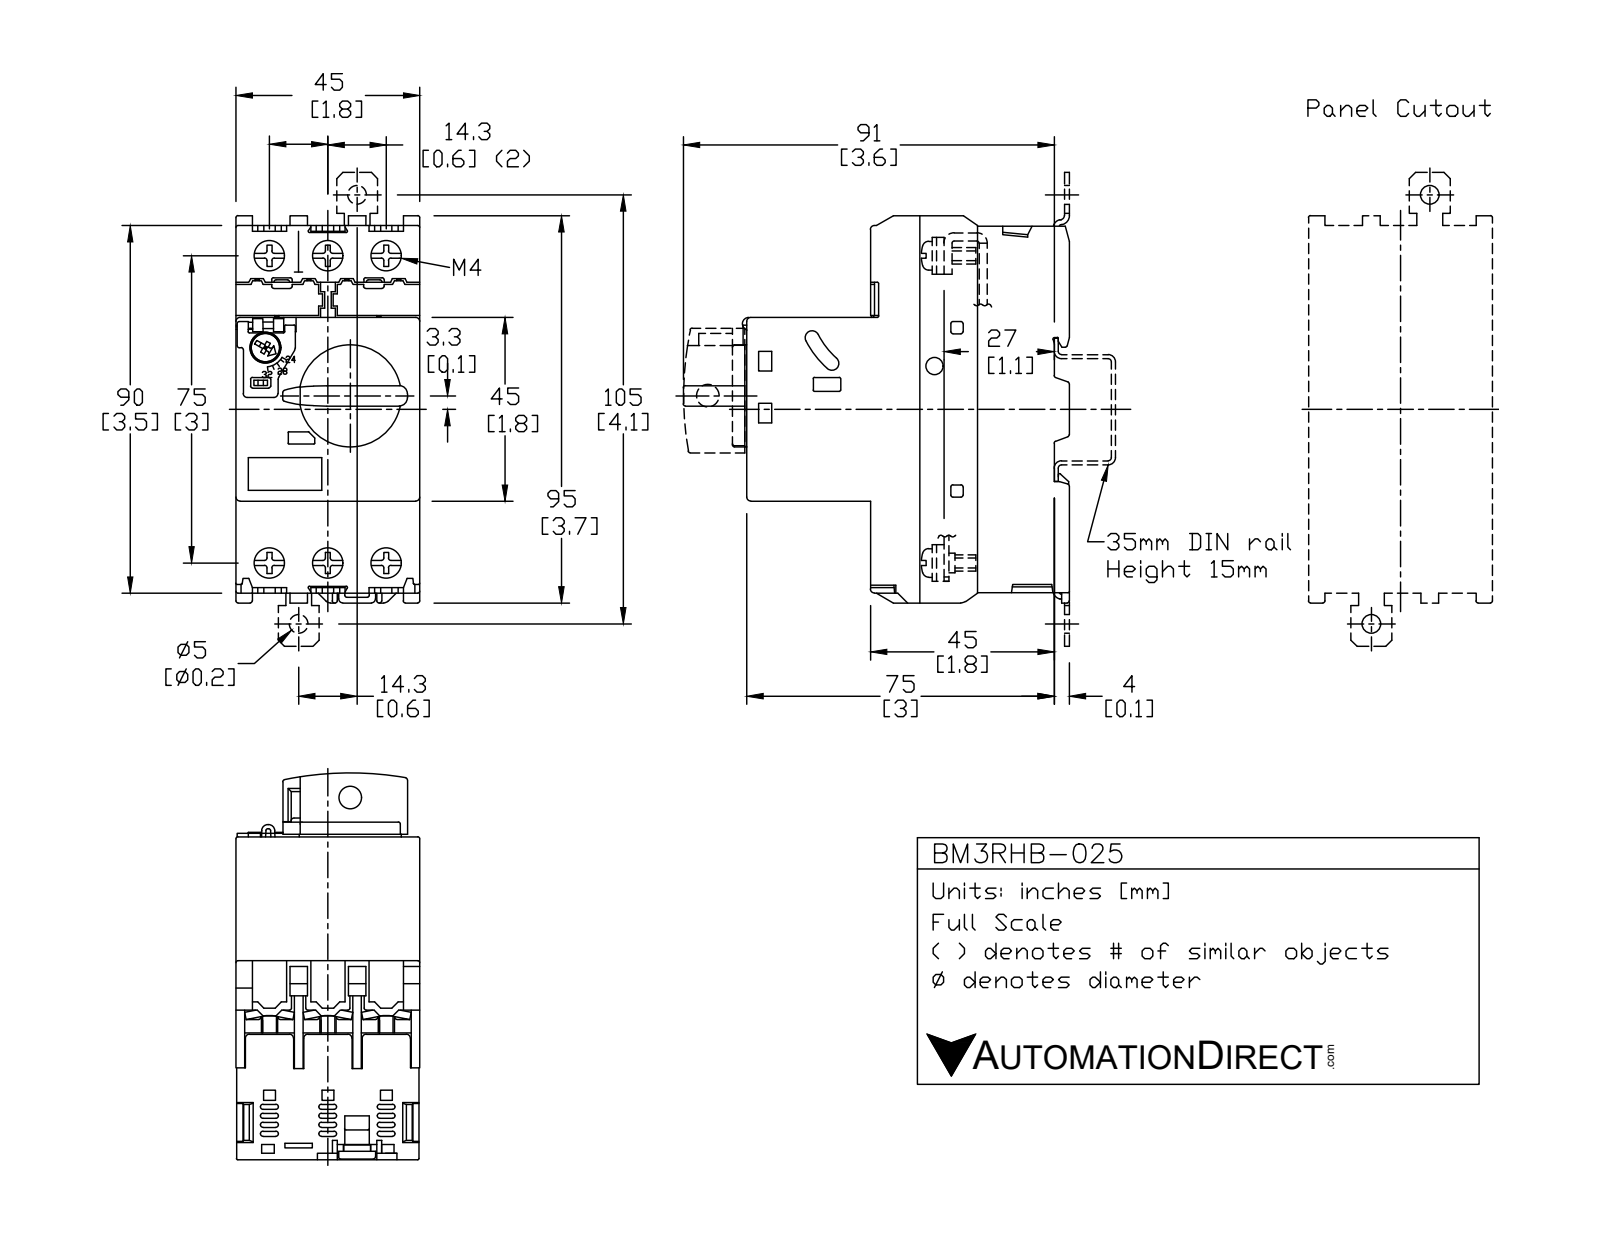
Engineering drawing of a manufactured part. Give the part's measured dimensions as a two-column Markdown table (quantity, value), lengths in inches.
| quantity | value |
| --- | --- |
| part name | BM3RHB-025 |
| STEP written by | SolidWorks 2018 (AUTOMOTIVE_DESIGN) |
| units | inches |
| bodies | 25 solids, 1294 faces (964 planar, 327 cylindrical, 3 other) |
| overall size | 3.732 × 3.72 × 1.772 |
| volume | 14.13 in³ |
| surface area | 88.41 in² |
| round holes (diameter × count) | 0.157 × 6, 0.291 × 6, 0.063 × 1, 0.165 × 1, 0.197 × 1, 0.217 × 1, 0.295 × 1 |
| round bosses / shafts (diameter × count) | 0.236 × 6, 0.984 × 1, 0.276 × 1 |
| partial cylindrical surfaces (radius × count) | 0.02 × 67, 0.024 × 24, 0.079 × 14, 0.012 × 12, 0.039 × 8, 0.098 × 8, 0.008 × 6, 0.059 × 2 |
| main face-to-face distances | 1.772, 1.441, 1.669, 3.11, 0.882, 2.654, 0.118, 0.65, 0.791, 0.472 |
| hole center spacings | 0.563, 3.006, 2.953, 1.126, 3.16, 0.883, 0.941, 1.068 |
